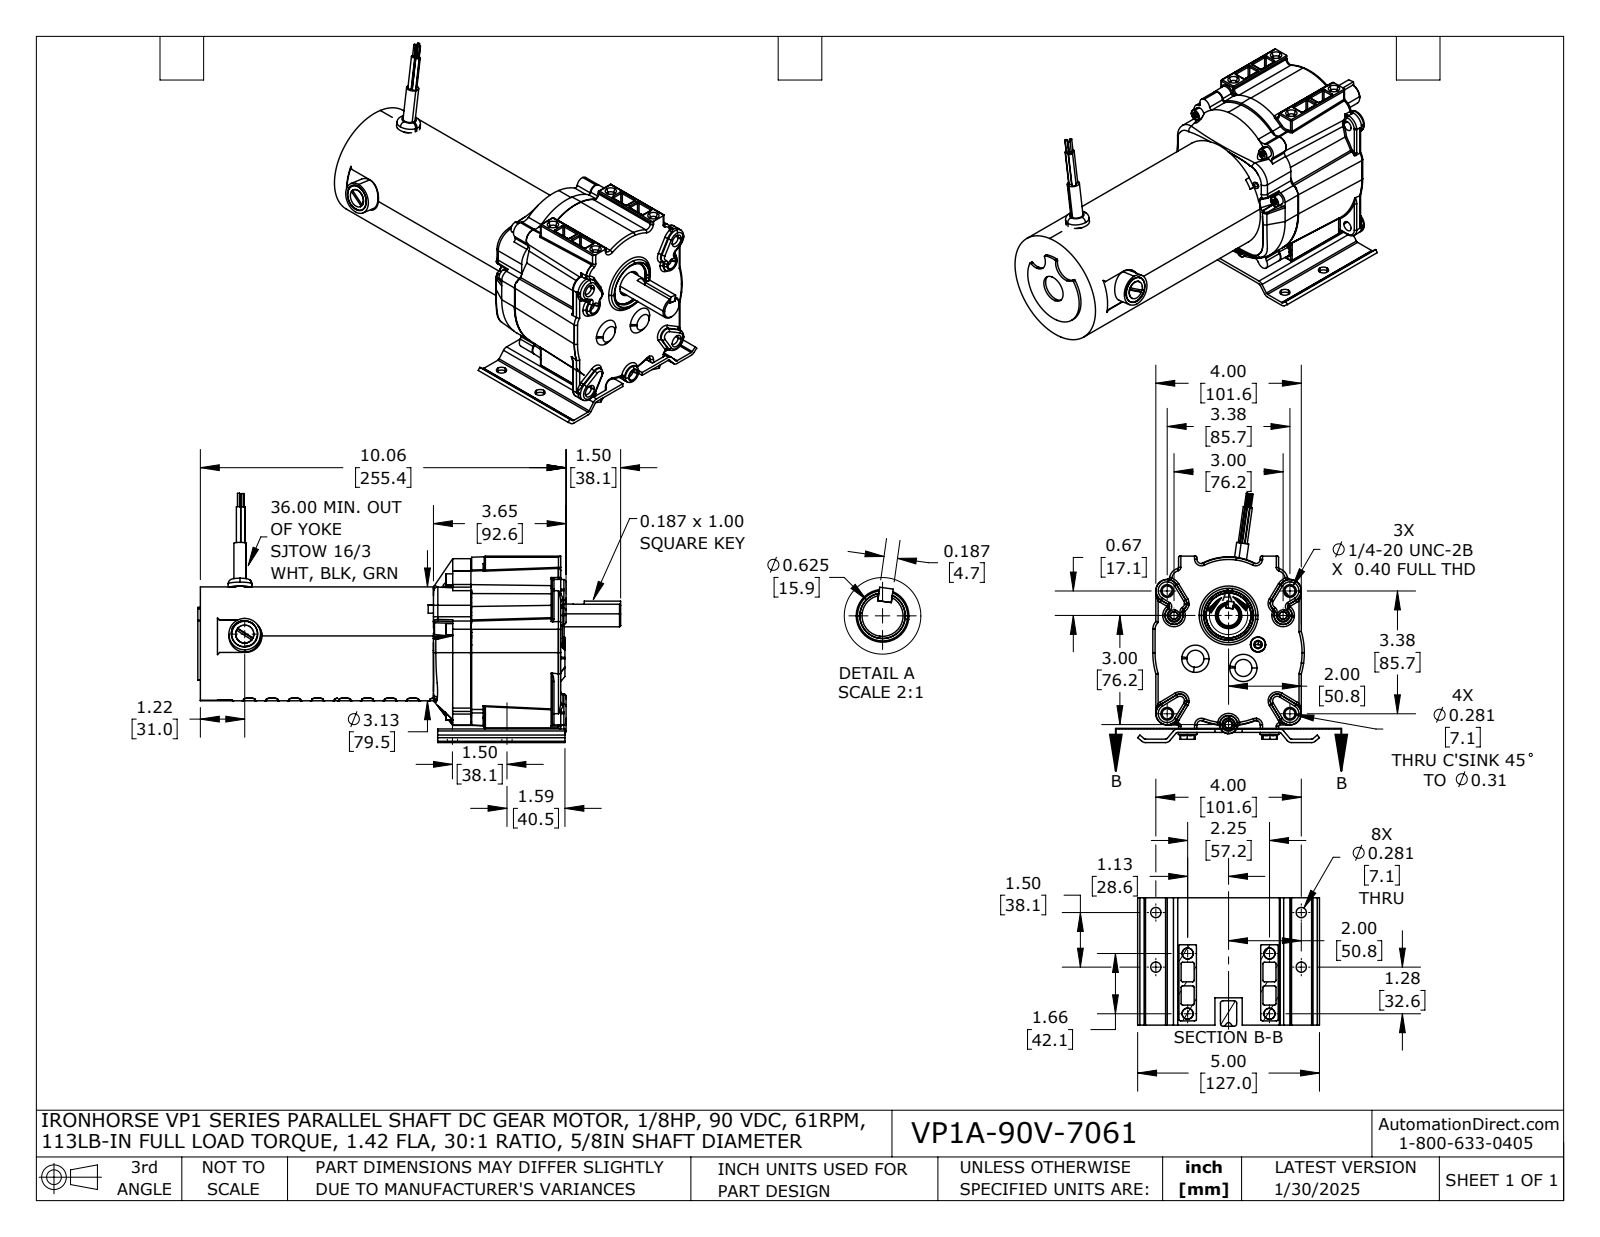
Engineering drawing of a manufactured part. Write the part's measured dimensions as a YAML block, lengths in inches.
part_name: "VP1A-90V-7061"
step_written_by: "SolidWorks 2024 (AUTOMOTIVE_DESIGN)"
units: inches
bodies: {solids: 10, faces: 2472, planar: 654, cylindrical: 701, other: 1117}
overall_size: [11.627, 6.854, 5]
volume: 98.93
surface_area: 345.4
round_holes:
  - {diameter: 0.281, count: 12}
  - {diameter: 0.218, count: 5}
  - {diameter: 0.159, count: 3}
  - {diameter: 0.207, count: 3}
  - {diameter: 0.135, count: 2}
  - {diameter: 0.166, count: 2}
  - {diameter: 0.204, count: 2}
  - {diameter: 0.397, count: 2}
  - {diameter: 0.688, count: 2}
  - {diameter: 0.875, count: 2}
  - {diameter: 0.75, count: 1}
  - {diameter: 0.813, count: 1}
round_bosses_or_shafts:
  - {diameter: 0.307, count: 5}
  - {diameter: 0.19, count: 5}
  - {diameter: 0.51, count: 4}
  - {diameter: 0.3, count: 4}
  - {diameter: 0.12, count: 3}
  - {diameter: 0.06, count: 3}
  - {diameter: 0.873, count: 2}
  - {diameter: 0.733, count: 2}
partial_cylinders:
  - {radius: 0.03, count: 52}
  - {radius: 0.031, count: 38}
  - {radius: 0.062, count: 23}
  - {radius: 0.12, count: 18}
  - {radius: 0.156, count: 18}
  - {radius: 0.19, count: 10}
  - {radius: 0.151, count: 9}
  - {radius: 0.161, count: 9}
face_to_face_distances: [0.095, 2.449, 3.5, 1.051, 9.44, 6.991, 5.94, 0.47, 6.97, 9.91]
hole_center_spacings: [1.5, 3.375, 1.691, 0.492, 0.698, 1.224, 1.426, 1.552]
